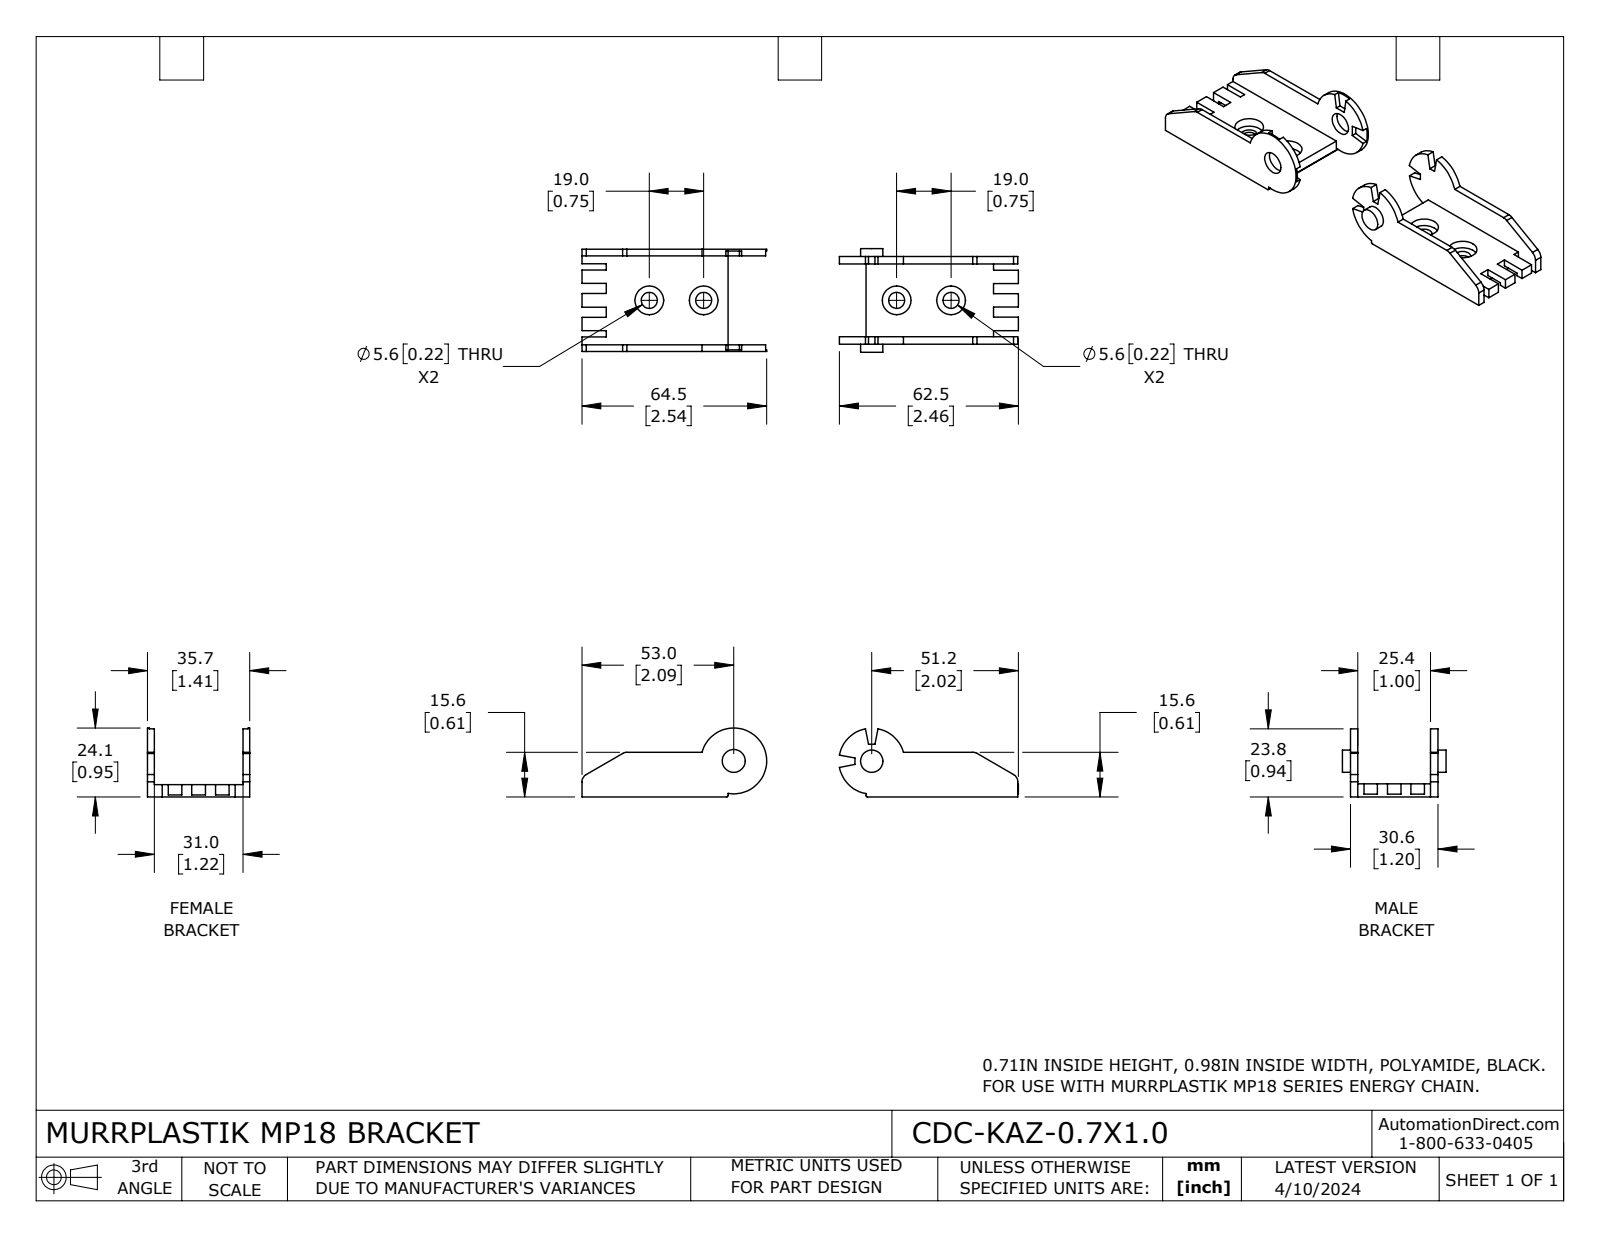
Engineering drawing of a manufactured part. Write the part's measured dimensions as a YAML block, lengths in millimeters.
part_name: "CDC-KAZ-0.7X1.0; CDC-KAZ-0.7X1.0_Male; CDC-KAZ-0.7X1.0_FEMALE"
step_written_by: "SolidWorks 2023 (CONFIG_CONTROL_DESIGN)"
units: millimeters
bodies: {solids: 2, faces: 143, planar: 100, cylindrical: 43, other: 0}
overall_size: [152.4, 36.2, 24.1]
volume: 20450
surface_area: 15600
round_holes:
  - {diameter: 5.6, count: 4}
  - {diameter: 10, count: 4}
  - {diameter: 8, count: 1}
round_bosses_or_shafts:
  - {diameter: 7.8, count: 1}
partial_cylinders:
  - {radius: 3, count: 4}
  - {radius: 0.5, count: 2}
  - {radius: 11.5, count: 2}
face_to_face_distances: [2.5, 33.1, 2.8, 2.6, 5.2, 30.6, 28, 30.8, 2.4, 33.4]
hole_center_spacings: [19, 86.4, 67.4, 105.4]
